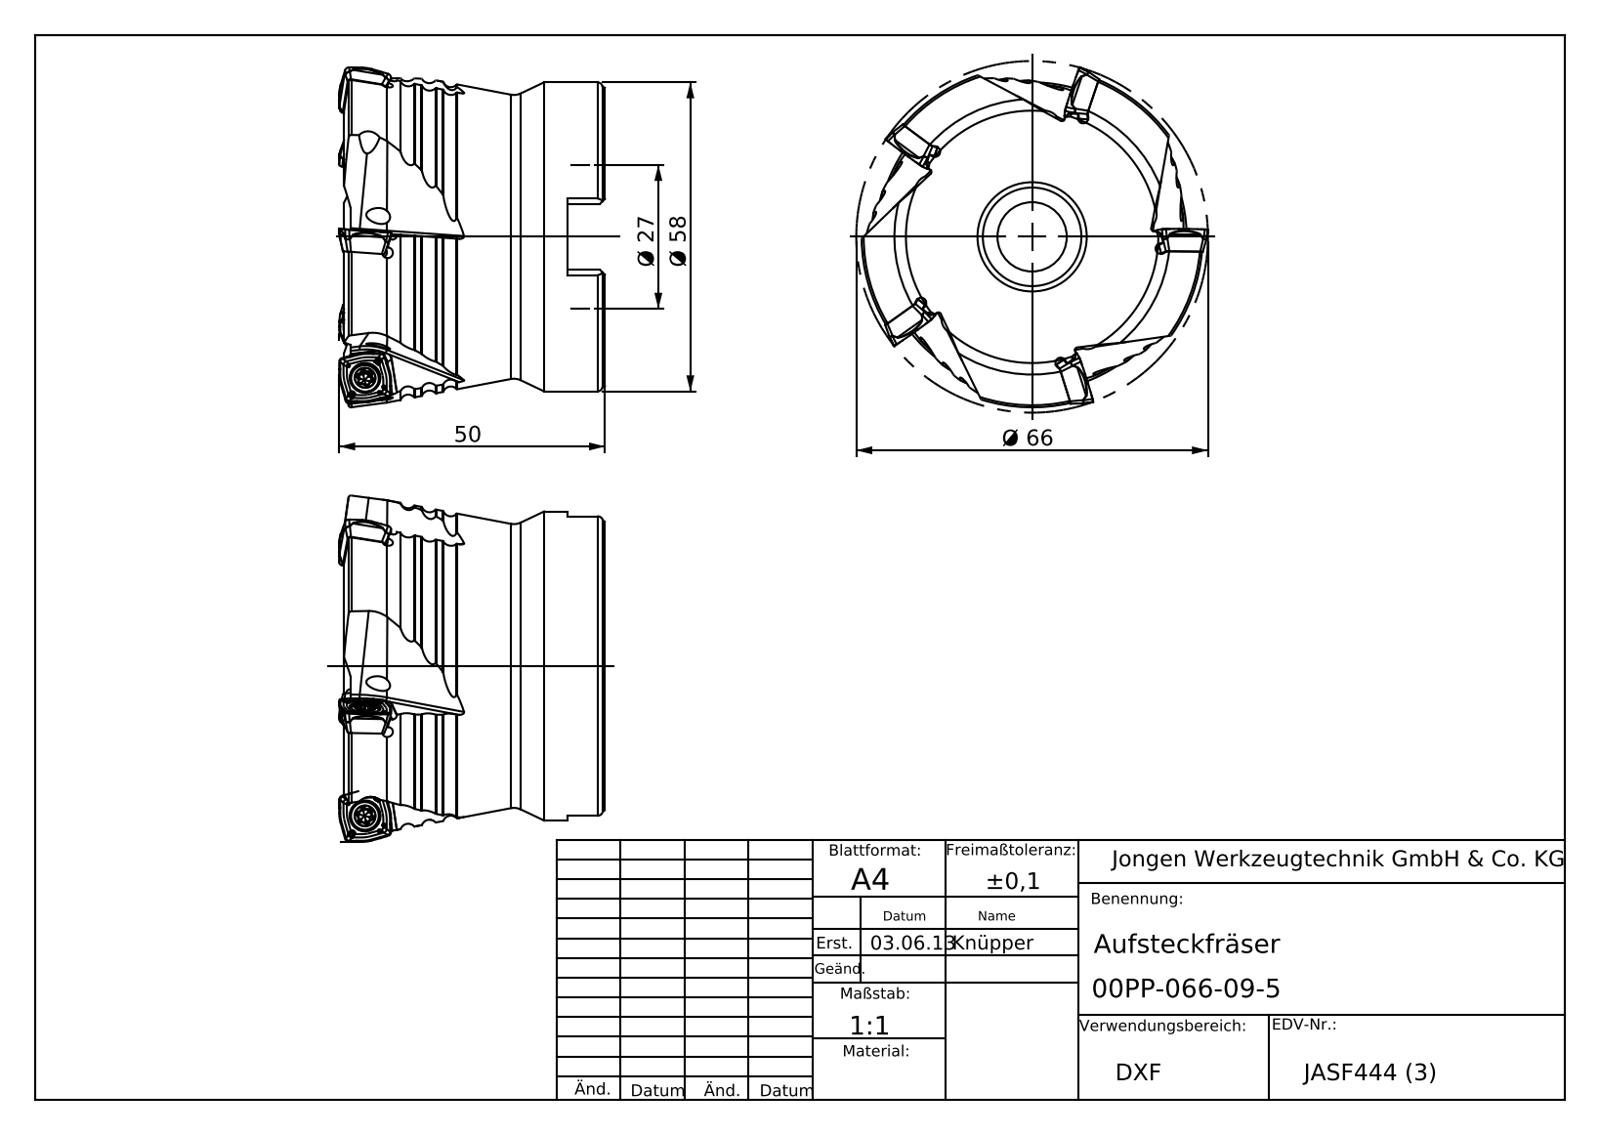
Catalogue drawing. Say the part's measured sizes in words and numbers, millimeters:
The part is named "00PP-066-09-5". Its 3-D file was written by "SolidWorks 2013 (AUTOMOTIVE_DESIGN)". It is 1 solid with 236 faces: 74 planar, 51 cylindrical and 111 other. Overall it measures 66.03 by 66.03 by 49.91 millimeters. Its volume is 107 981 cubic millimeters and its surface area 20 805 square millimeters. Round holes: 5 of diameter 3, 1 of diameter 13, 1 of diameter 18.5, 1 of diameter 26.8, 1 of diameter 27.15, 1 of diameter 27.3. Round bosses or shafts: 1 of diameter 58. Partial cylindrical surfaces (rounded edges, fillets, slot ends): 10 of radius 0.5, 10 of radius 0.8, 10 of radius 1, 5 of radius 2. The main face-to-face distances are 47.75, 7, 40.75, 12.4, 34, 27, 13.75, 22, 15, 12.
